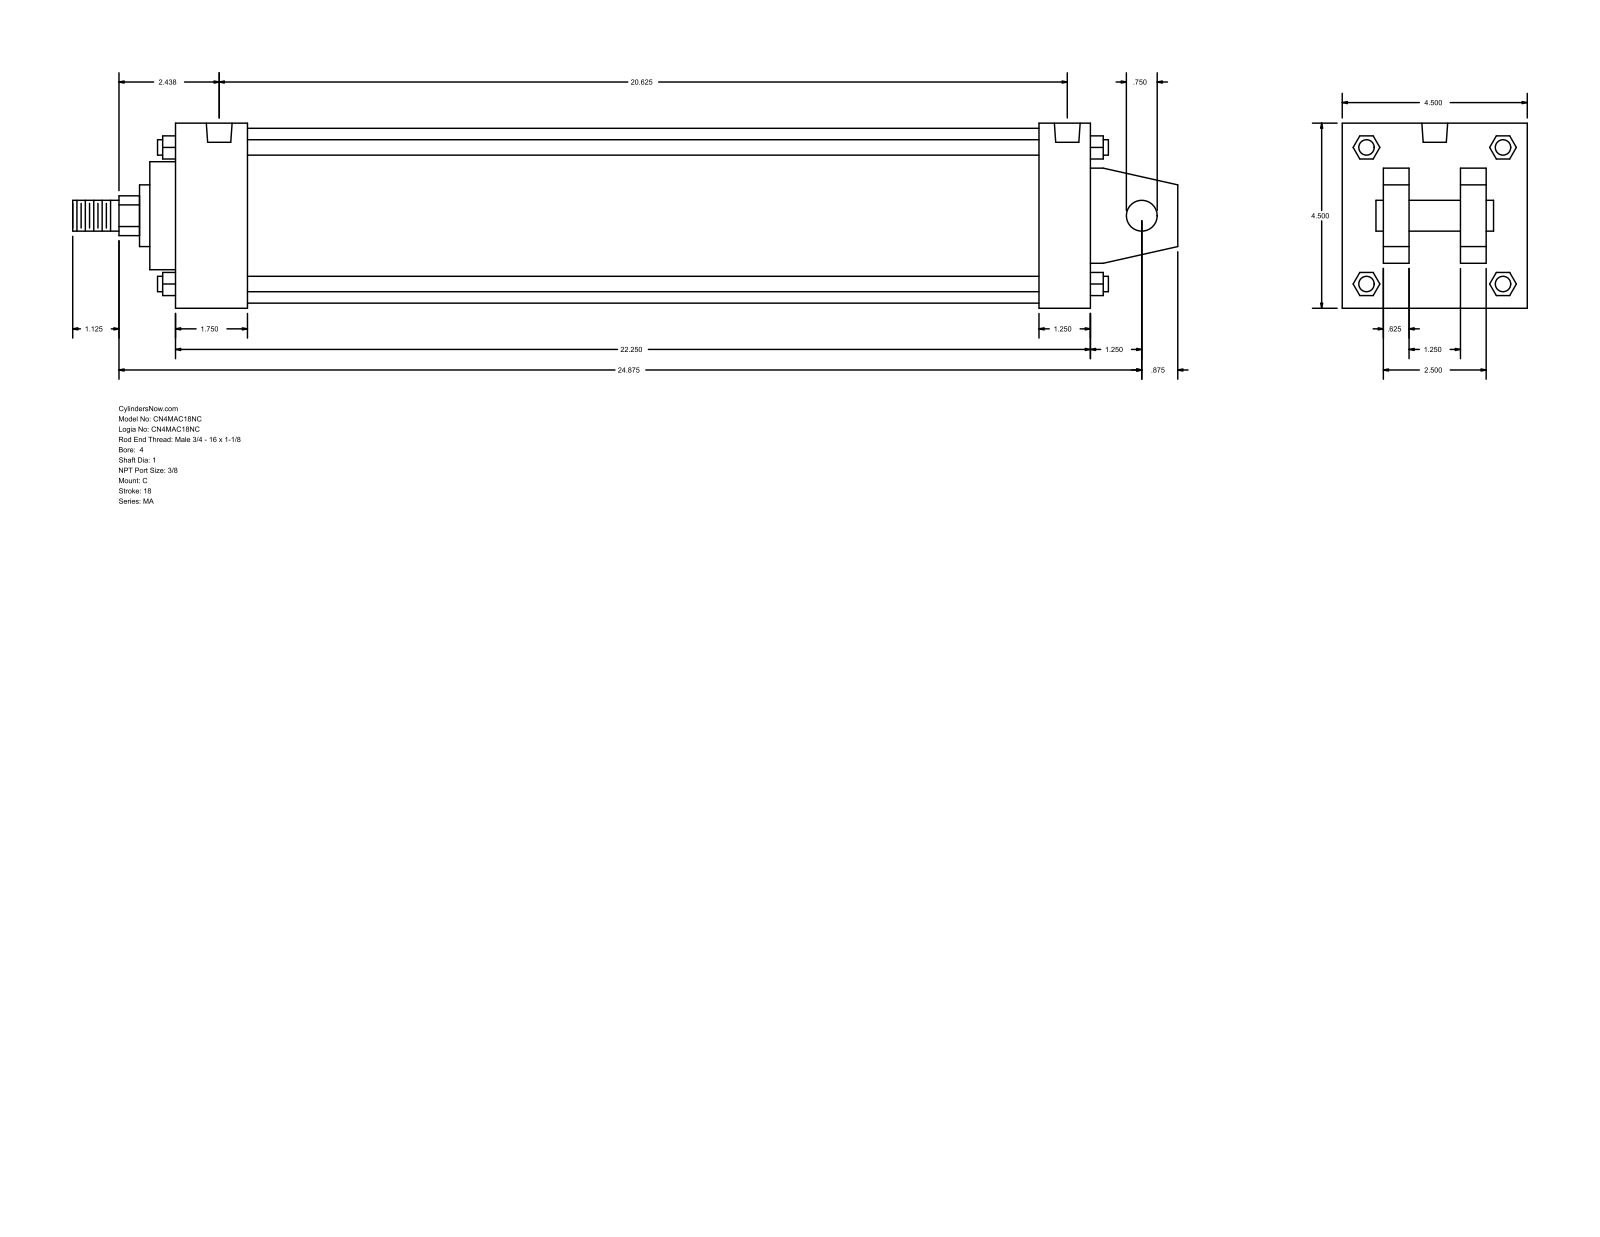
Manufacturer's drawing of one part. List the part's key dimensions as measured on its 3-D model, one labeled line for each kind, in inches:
Part name (STEP PRODUCT): MA_C__0400_1
STEP written by: GSSL Pune (CONFIG_CONTROL_DESIGN)
Units: inches
Bodies: 0 solids, 141 faces (109 planar, 32 cylindrical, 0 other)
Overall size (bounding box): 26.875 × 4.5 × 4.5
Round holes (diameter × count): ⌀0.437 ×4, ⌀0.627 ×2
Round bosses / shafts (diameter × count): ⌀0.375 ×4, ⌀0.75 ×2, ⌀4.25 ×1, ⌀2.625 ×1, ⌀1.5 ×1, ⌀1 ×1
Partial cylindrical surfaces — rounded edges, fillets, slot ends (radius × count): R0.484 ×1
Main face-to-face distances: 4.5, 22.25, 0.625, 2.875, 1.625, 1, 3.5, 1.875, 21, 1.25
Hole centre spacings: 20.25, 0.187, 0.188, 20.437, 20.438, 20.625
